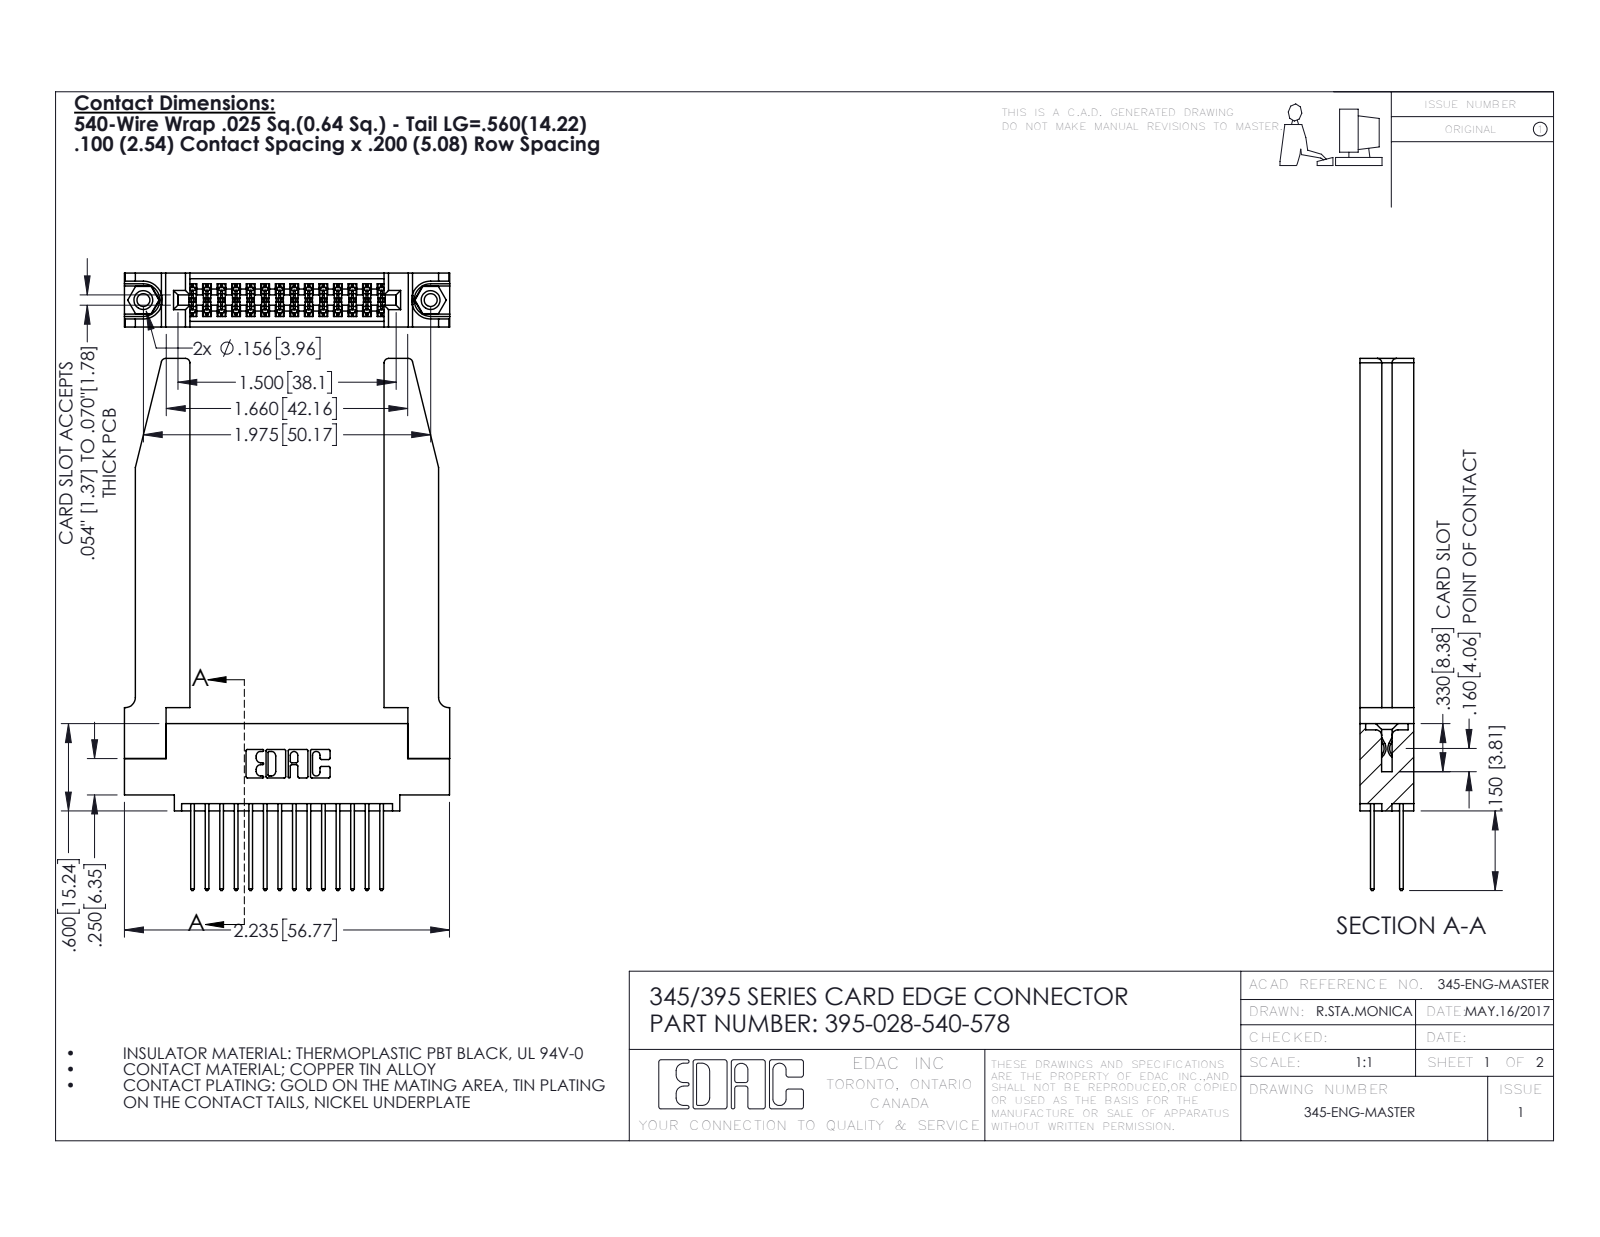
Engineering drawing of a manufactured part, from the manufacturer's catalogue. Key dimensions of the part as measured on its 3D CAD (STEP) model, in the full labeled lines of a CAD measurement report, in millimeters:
Part name (STEP PRODUCT): 345 Part_0.110 Offset - 0.156 Dia-TH; 345-292-001_345-293-140; 345-250-001_345-250-001-102; 395-028-540-578 (+1 more)
STEP written by: SolidWorks 2016 (CONFIG_CONTROL_DESIGN)
Units: millimetres
Bodies: 33 solids, 1764 faces (1150 planar, 562 cylindrical, 52 other)
Overall size (bounding box): 92.9 × 56.8 × 9.4
Volume: 13 100 mm³ · Surface area: 14 700 mm²
Round holes (diameter × count): ⌀2.3 ×2, ⌀3.2 ×2, ⌀4 ×2, ⌀1.6 ×1
Round bosses / shafts (diameter × count): ⌀3.9 ×2
Partial cylindrical surfaces — rounded edges, fillets, slot ends (radius × count): R0.2 ×42, R0.3 ×28, R0.3 ×22, R0.8 ×8, R0.2 ×6, R0.8 ×6, R0.7 ×3, R0.4 ×2
Main face-to-face distances: 9.4, 1.8, 7.6, 5.1, 2.5, 6.9, 0.6, 3.8, 3.8, 5.7
Hole centre spacings: 6.9, 44.2, 50.2
